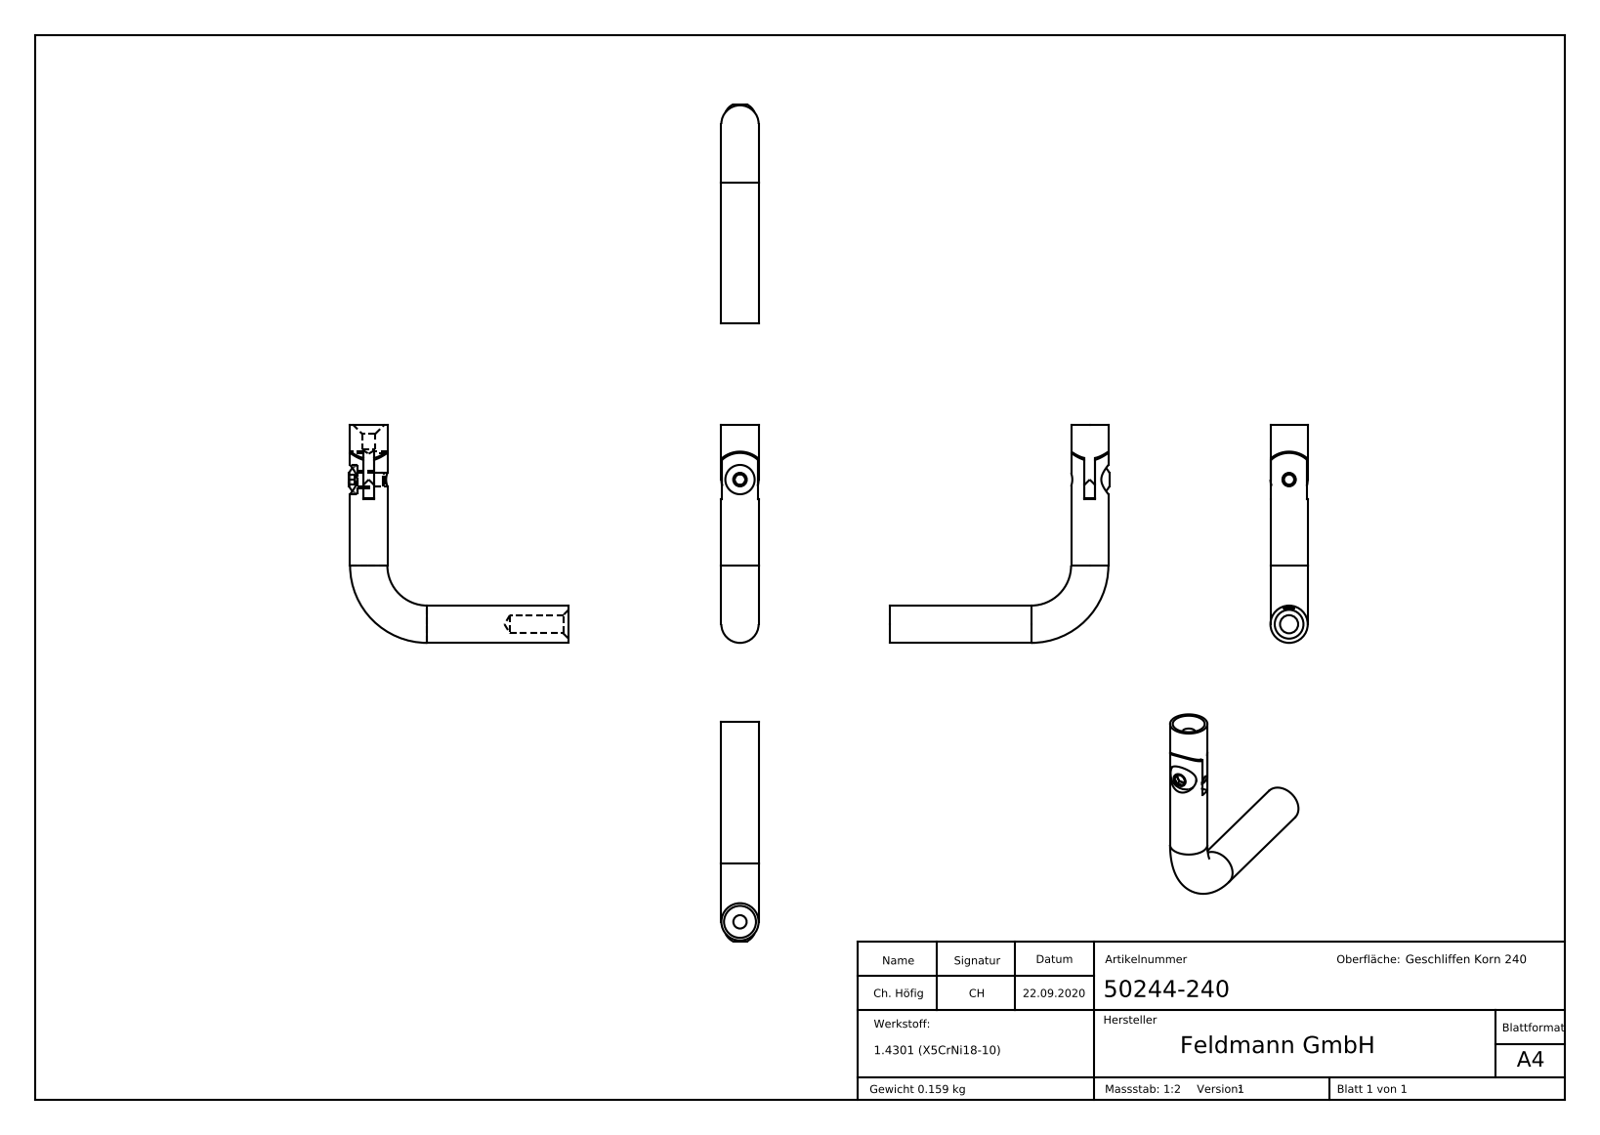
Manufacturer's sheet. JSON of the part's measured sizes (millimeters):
{"part_name": "50244-240; 50244-240 Teil2_50244-240 Teil2; 50244-240 Teil2; 50244-240 Teil1 (+3 more)", "step_written_by": "SolidWorks 2018 (CONFIG_CONTROL_DESIGN)", "units": "millimeters", "bodies": {"solids": 3, "faces": 294, "planar": 158, "cylindrical": 27, "other": 109}, "overall_size": [82.35, 82, 14], "volume_mm3": 20083, "surface_area_mm2": 8699, "round_holes": [[5, 2], [6.5, 1], [6.8, 1], [11, 1]], "round_bosses_or_shafts": [[14, 2], [4.77, 1]], "partial_cylinders_radius": [[7, 1], [10, 1], [10.5, 1]], "face_to_face_distances": [4.05, 4.1, 4, 2, 2.05, 6.05, 6.1, 79.05, 77.05, 77], "hole_center_spacings": [54.3]}
